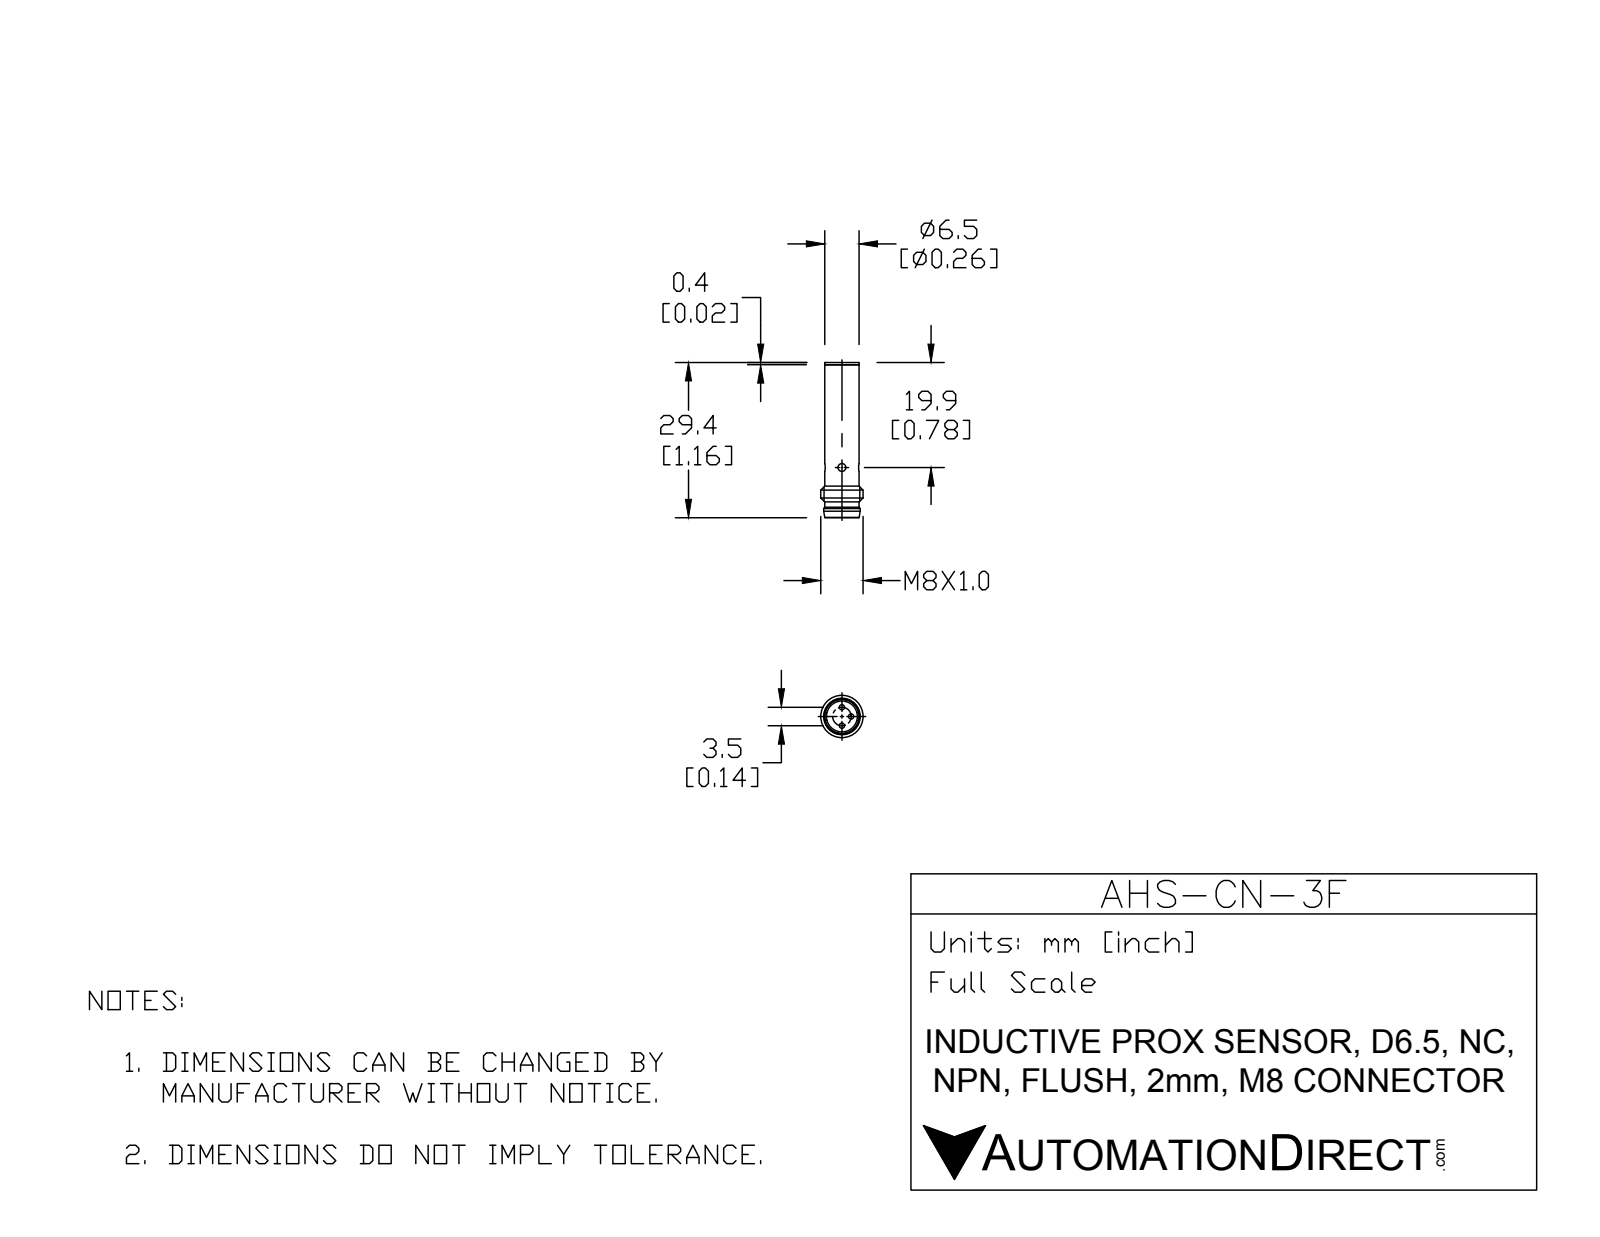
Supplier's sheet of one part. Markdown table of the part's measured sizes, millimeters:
| quantity | value |
| --- | --- |
| part name | AHS-CN-3F |
| STEP written by | SolidWorks 2015 (CONFIG_CONTROL_DESIGN) |
| units | millimeters |
| bodies | 4 solids, 56 faces (12 planar, 26 cylindrical, 18 other) |
| overall size | 29.4 × 8 × 8 |
| volume | 891 mm³ |
| surface area | 842 mm² |
| round holes (diameter × count) | 1.5 × 2, 5.85 × 1 |
| round bosses / shafts (diameter × count) | 1 × 3, 8 × 1, 6.9 × 1, 6.5 × 1 |
| main face-to-face distances | 24.4, 3, 27.4, 5.5, 2, 5, 29.4, 29, 27, 24 |
